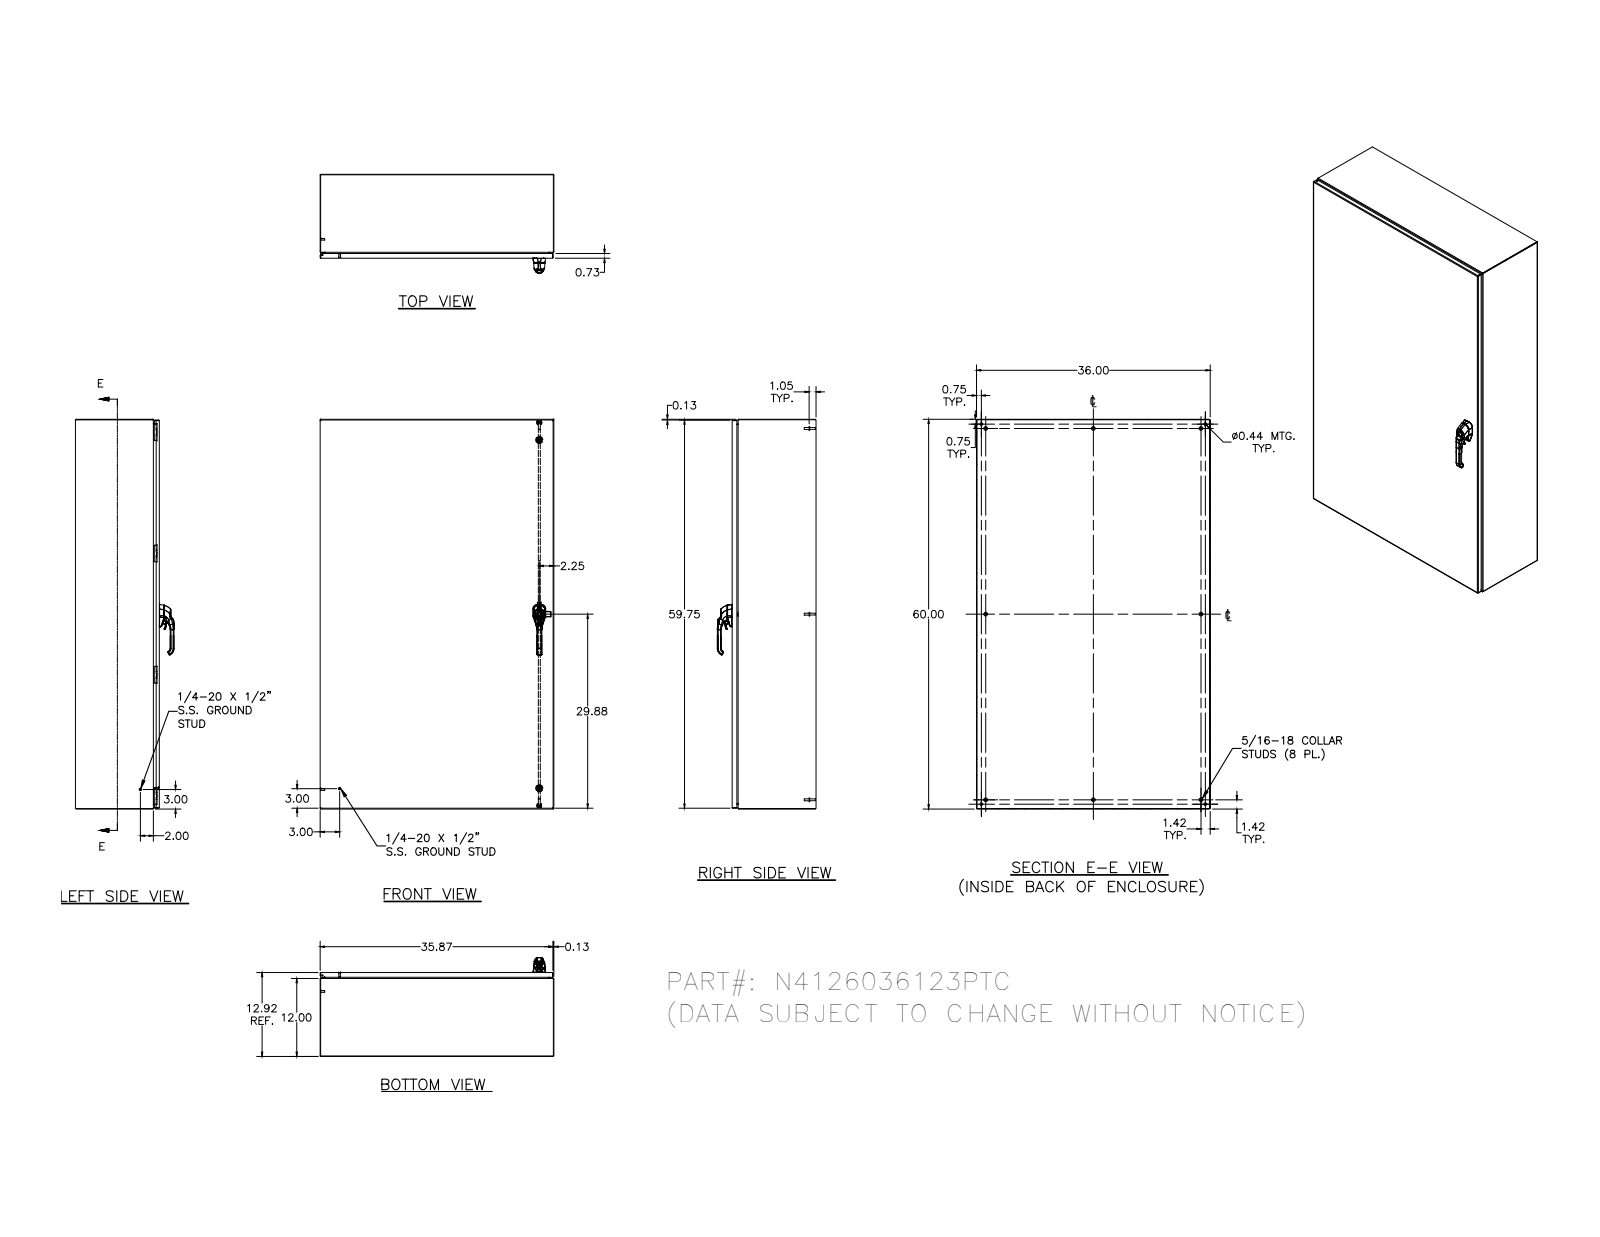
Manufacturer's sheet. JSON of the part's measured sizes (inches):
{"part_name": "N4126036123PTC; N4126036123PTCBLR; N41236123PTCTB; HFW328176 (+8 more)", "step_written_by": "Autodesk Inventor 2011 (AUTOMOTIVE_DESIGN)", "units": "inches", "bodies": {"solids": 73, "faces": 3840, "planar": 1221, "cylindrical": 1441, "other": 1178}, "overall_size": [60, 36, 15.186], "volume_in3": 523.8, "surface_area_in2": 14233, "round_holes": [[0.188, 9], [0.093, 8], [0.152, 8], [0.167, 8], [0.172, 8], [0.156, 4], [0.165, 4], [0.197, 4], [0.438, 4], [0.213, 3], [0.236, 3], [0.354, 3]], "round_bosses_or_shafts": [[0.25, 18], [0.563, 8], [0.36, 8], [0.32, 8], [0.3, 8], [0.275, 8], [0.256, 8], [0.164, 8]], "partial_cylinders_radius": [[0.02, 174], [0.012, 78], [0.05, 50], [0.031, 36], [0.016, 34], [0.118, 28], [0.125, 28], [0.019, 19]], "face_to_face_distances": [0.074, 12.843, 12.769, 12.917, 35.926, 59.926, 35.852, 36, 59.852, 60], "hole_center_spacings": [18.667, 37.333, 56, 0.66, 0.017, 0.5, 18.659, 18.667]}
